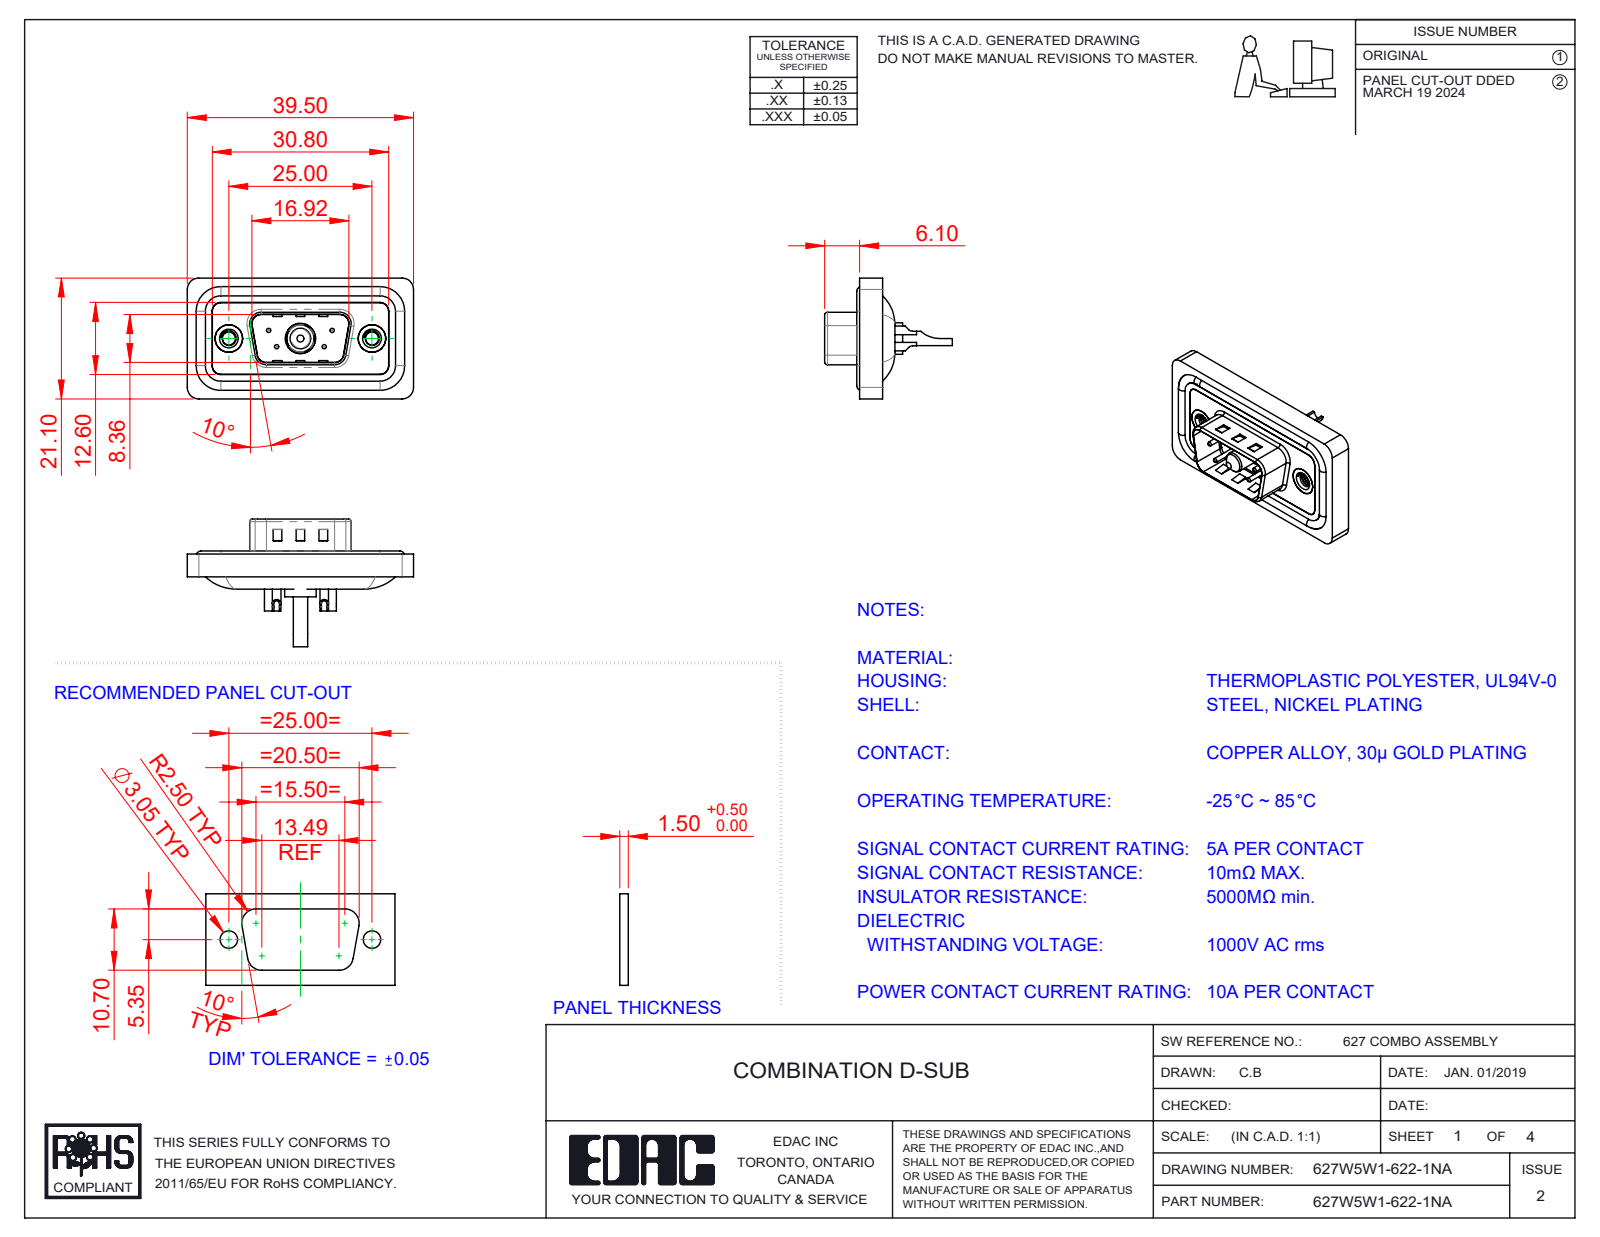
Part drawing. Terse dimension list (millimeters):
name: 627Combo Contact Row 2_22; 627Combo Shell Front_09 Contacts; 627Combo Waterproof Housing_09 Contacts; 627Combo Contact Row 1_22 (+5 more)
written by: SolidWorks 2023 (CONFIG_CONTROL_DESIGN)
unit: mm
bodies: 13 solids, 602 faces (193 planar, 268 cylindrical, 141 other)
size: 39.5 × 22.3 × 21.1
volume: 4 393 mm³; area: 7 018 mm²
holes: 4× ⌀0.75, 4× ⌀1, 4× ⌀1.6, 4× ⌀2, 2× ⌀2.26, 2× ⌀4, 2× ⌀4.8, 2× ⌀5, 1× ⌀1.7, 1× ⌀4.85, 1× ⌀5.3
bosses: 4× ⌀1.6, 4× ⌀1.5, 2× ⌀4.9, 1× ⌀5.5, 1× ⌀5.2, 1× ⌀4.75, 1× ⌀3.75, 1× ⌀3.6
rounds: 22× R1.5, 18× R2, 8× R0.5, 8× R1.6, 6× R1, 4× R0.25, 4× R0.6, 4× R0.65
face distances: 0.4, 1.1, 2.9, 1.6, 1.5, 3.1, 0.5, 2.5, 4, 0.8
hole spacings: 3.16, 5.72, 7.1, 12.5, 18.1, 4.39, 4.4, 8.31
